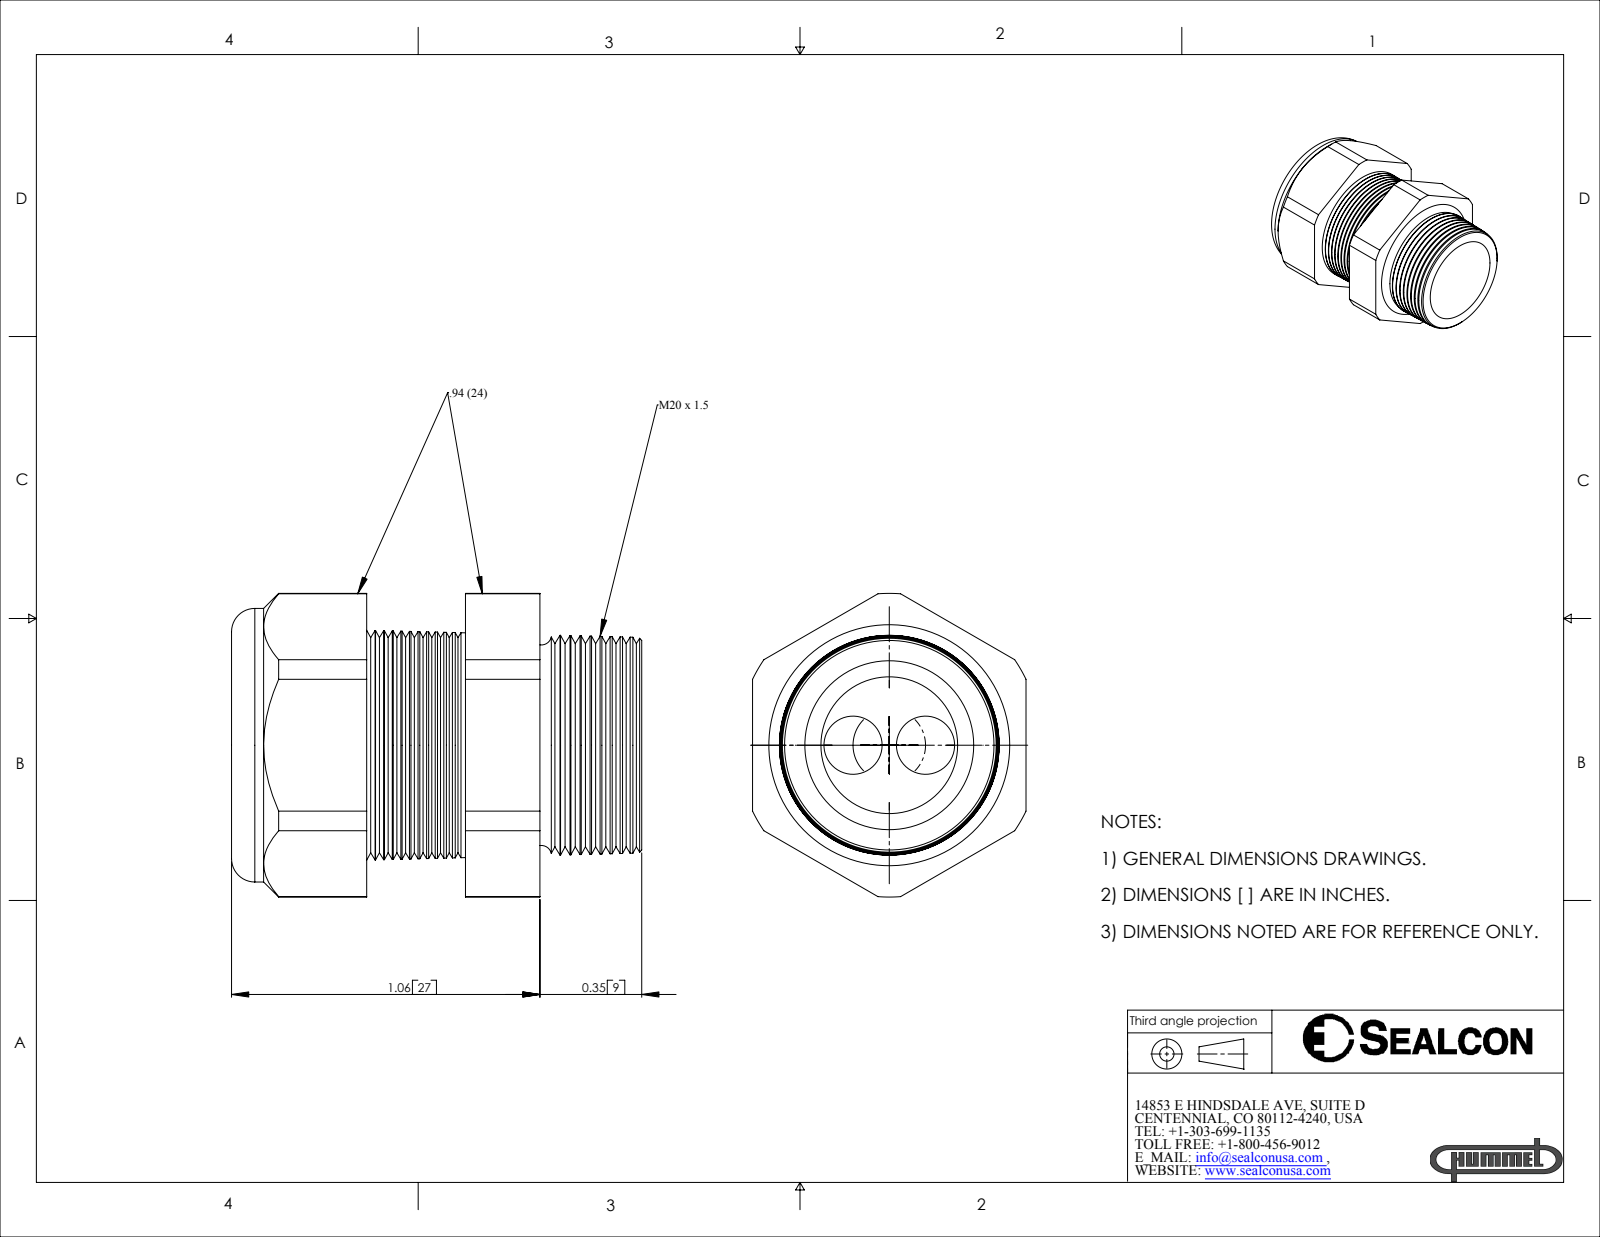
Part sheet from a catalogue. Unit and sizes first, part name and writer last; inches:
Units: inches
Overall size (bounding box): 1.41 × 1.043 × 0.94
Round holes (diameter × count): ⌀0.2 ×2, ⌀0.45 ×1, ⌀0.47 ×1
Round bosses / shafts (diameter × count): ⌀0.94 ×1
Partial cylindrical surfaces — rounded edges, fillets, slot ends (radius × count): R0.522 ×1
Main face-to-face distances: 0.94, 0.804, 0.465, 0.34, 1.06, 0.596, 0.256, 1.41, 0.946, 0.606
Hole centre spacings: 0.124, 0.249
Volume: 0.571 in³ · Surface area: 9.904 in²
Bodies: 2 solids, 178 faces (20 planar, 24 cylindrical, 134 other)
Part name (STEP PRODUCT): CD20M4-GY
STEP written by: SolidWorks 2007 (CONFIG_CONTROL_DESIGN)
